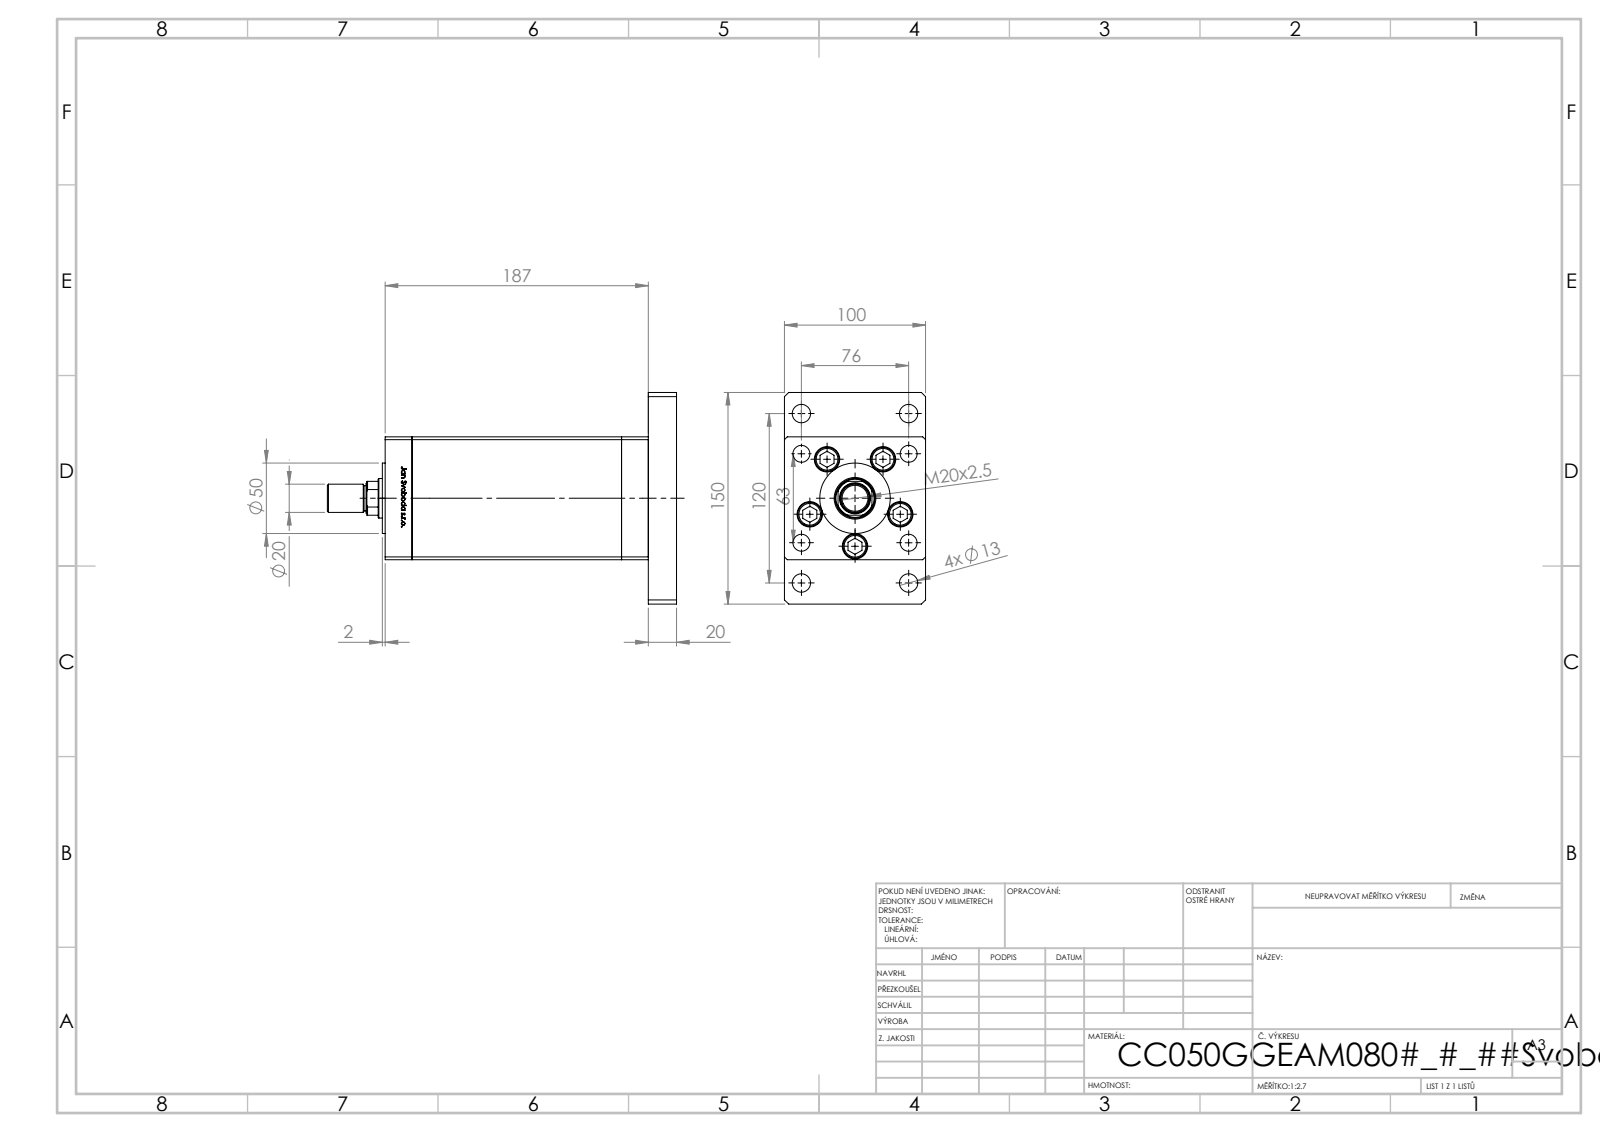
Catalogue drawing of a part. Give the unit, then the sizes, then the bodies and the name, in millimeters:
Units: millimetres
Overall size (bounding box): 247.5 × 150 × 100
Round holes (diameter × count): ⌀12 ×9, ⌀13.5 ×5, ⌀18 ×5, ⌀13 ×4, ⌀17 ×4, ⌀2 ×2, ⌀13.16 ×2, ⌀18.5 ×1, ⌀28 ×1, ⌀29.5 ×1, ⌀68 ×1
Round bosses / shafts (diameter × count): ⌀8 ×9, ⌀17 ×5, ⌀50 ×1, ⌀20 ×1, ⌀18 ×1
Partial cylindrical surfaces — rounded edges, fillets, slot ends (radius × count): R0.93 ×2, R13.5 ×1
Main face-to-face distances: 19, 100, 167.5, 87, 148.5, 20, 187.5, 39, 206.5, 186.5
Hole centre spacings: 34, 28.5, 49.36, 71.02, 76, 81.17, 91.5, 118.95
Volume: 1 706 000 mm³ · Surface area: 259 133 mm²
Bodies: 20 solids, 1324 faces (521 planar, 191 cylindrical, 612 other)
Part name (STEP PRODUCT): ALLEN BOLT; V220C_FRONT_G; V220C BACK_G; V220C_VC_G (+3 more)
STEP written by: SolidWorks 2019 (CONFIG_CONTROL_DESIGN)
